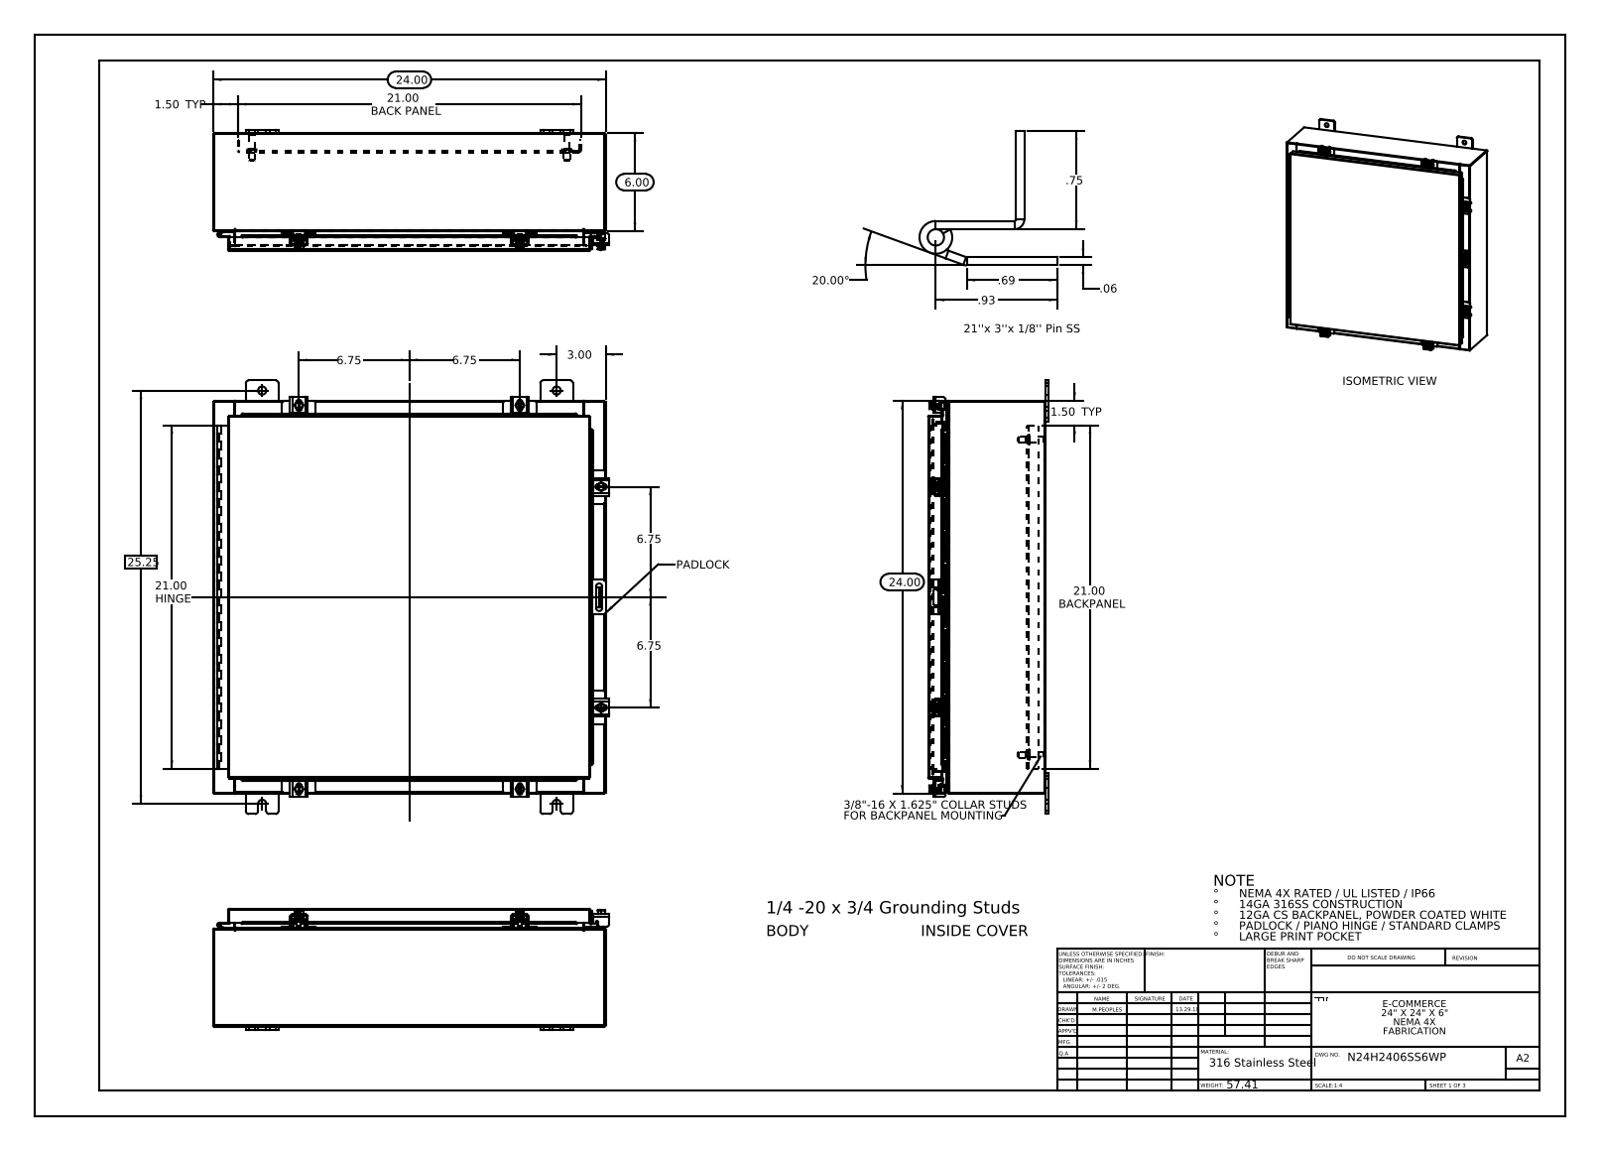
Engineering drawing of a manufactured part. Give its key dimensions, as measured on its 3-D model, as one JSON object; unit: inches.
{"part_name": "N24H2406SS6WP Hinge Cover Side; N24H2406SS6WP Body; Quarter-20 CD Stud; N24H2406SS6WP Standard Clamps (+8 more)", "step_written_by": "SolidWorks 2013 (CONFIG_CONTROL_DESIGN)", "units": "inches", "bodies": {"solids": 49, "faces": 1735, "planar": 914, "cylindrical": 713, "other": 108}, "overall_size": [26.5, 24.211, 7.389], "volume_in3": 202, "surface_area_in2": 5049, "round_holes": [[0.5, 8], [0.213, 6], [0.26, 6], [0.125, 2], [0.125, 1]], "round_bosses_or_shafts": [[0.25, 7], [0.5, 6], [0.399, 6], [0.625, 4], [0.375, 4], [0.33, 4], [0.315, 2], [0.236, 2]], "partial_cylinders_radius": [[0.06, 30], [0.013, 25], [0.19, 24], [0.088, 21], [0.12, 12], [0.141, 12], [0.125, 10], [0.05, 9]], "face_to_face_distances": [0.075, 7.126, 23.925, 7.051, 7.201, 0.104, 1, 1.075, 6.051, 6.126], "hole_center_spacings": [16.509, 19.134, 21.544, 26.907, 13.5, 1.858, 2.277, 2.423]}
